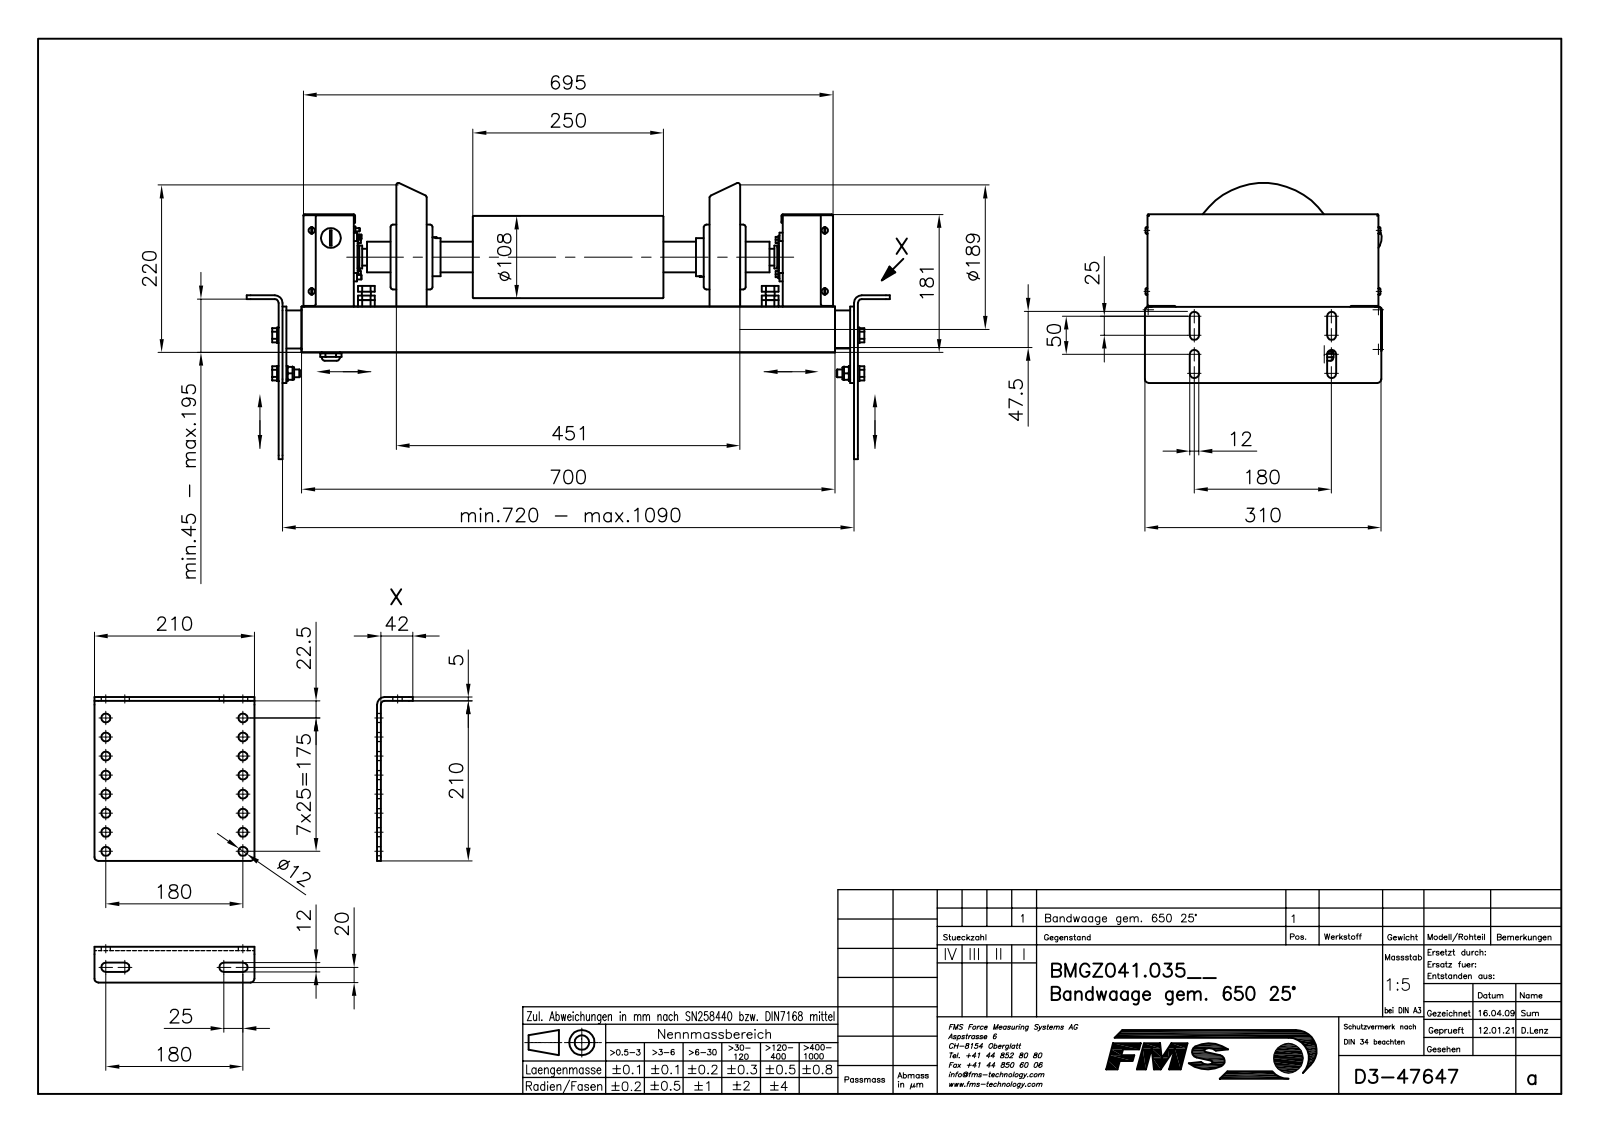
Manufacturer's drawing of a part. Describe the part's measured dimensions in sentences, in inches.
The part is named "B47647_STP; B50029; B46957; B4695602 (+8 more)". Its 3-D file was written by "Mechanical Desktop 2009 (CONFIG_CONTROL_DESIGN)". It is 161 solids with 2732 faces: 1379 planar, 974 cylindrical and 379 other. Overall it measures 33.228 by 14.261 by 12.232 inches. Its volume is 385.9 cubic inches and its surface area 4 924 square inches. Round holes: 17 of diameter 0.472, 6 of diameter 0.197, 4 of diameter 0.138, 4 of diameter 0.193, 4 of diameter 0.252, 4 of diameter 0.342, 4 of diameter 0.344, 4 of diameter 0.394, 4 of diameter 0.413, 4 of diameter 0.42, 4 of diameter 0.583, 3 of diameter 0.161. Round bosses or shafts: 11 of diameter 0.472, 8 of diameter 0.323, 8 of diameter 0.165, 6 of diameter 0.787, 6 of diameter 0.394, 5 of diameter 0.197, 4 of diameter 0.63, 4 of diameter 0.437. Partial cylindrical surfaces (rounded edges, fillets, slot ends): 34 of radius 0.079, 24 of radius 0.039, 16 of radius 0.157, 16 of radius 0.197, 14 of radius 0.236, 8 of radius 0.138, 6 of radius 0.089, 4 of radius 0.02. The main face-to-face distances are 0.157, 0.197, 0.039, 10.63, 1.417, 10.472, 1.26, 2.205, 10.787, 1.575. The hole center spacings are 0.984, 7.155, 1.969, 7.355, 2.953, 7.677, 3.937, 7.087.
